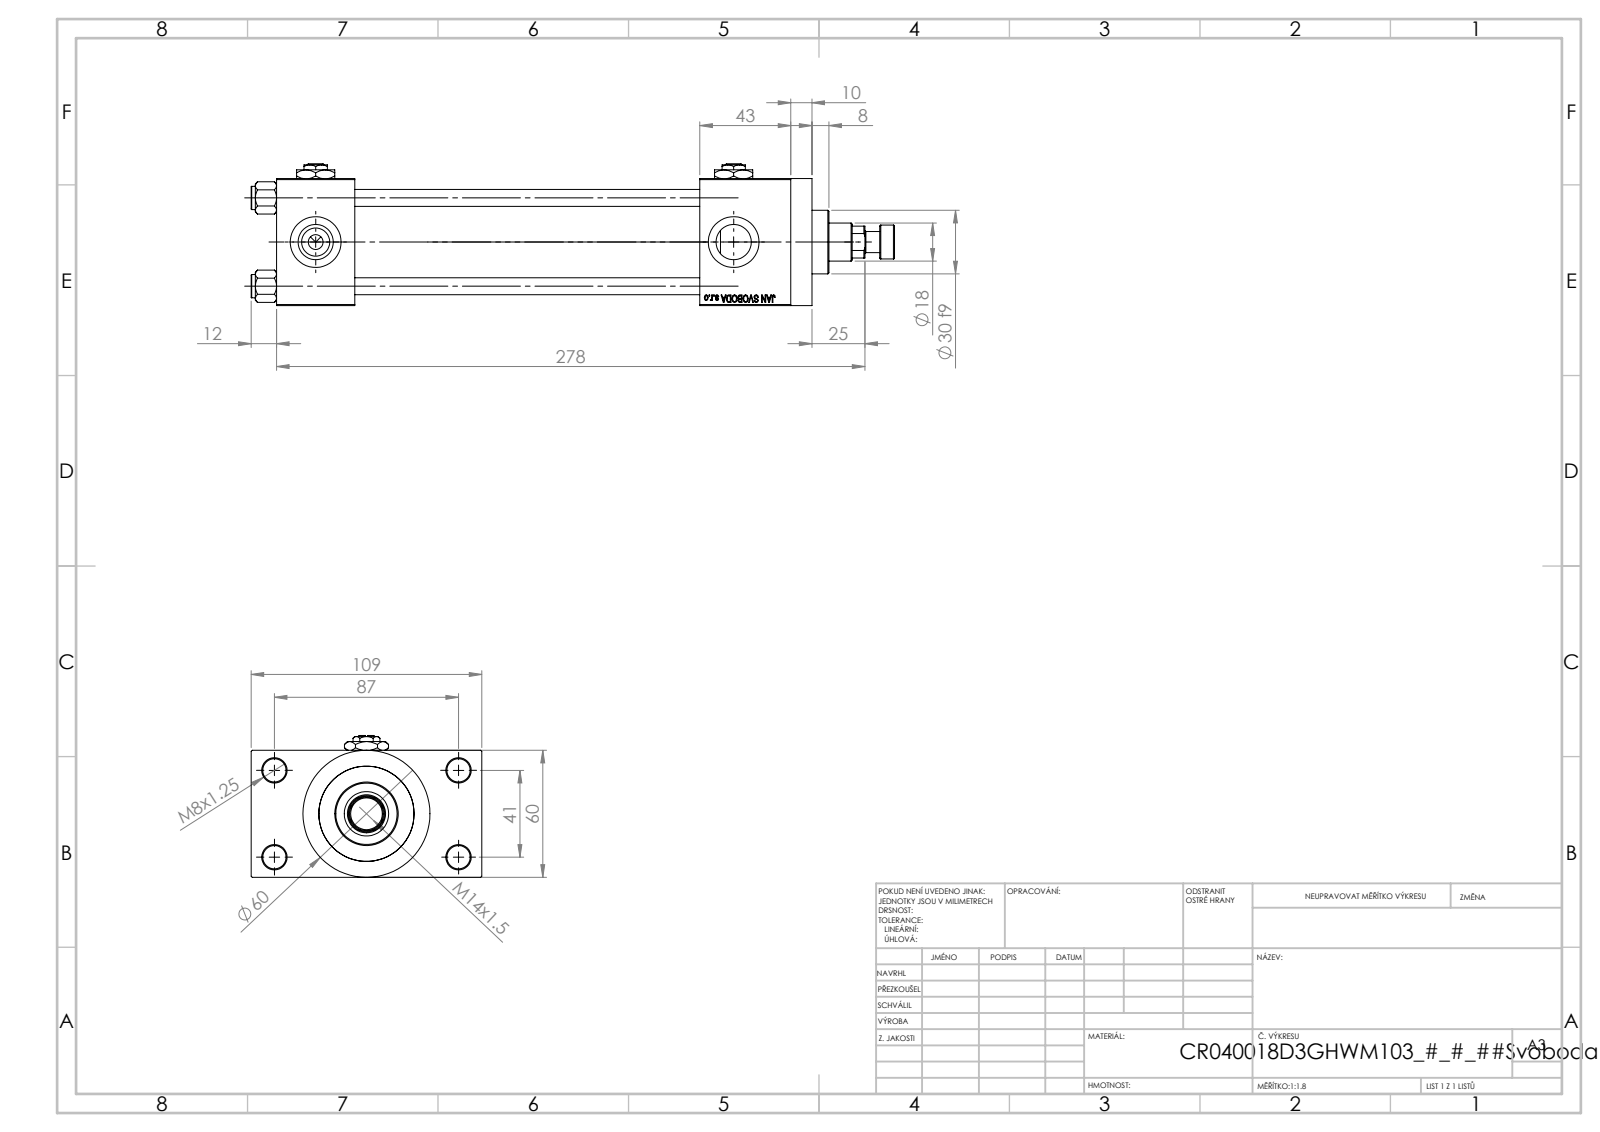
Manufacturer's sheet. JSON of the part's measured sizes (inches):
{"part_name": "NUT_M5_D; V215_VC_A; V215CR_ROD_END_W; V215CR_VCP_D (+3 more)", "step_written_by": "SolidWorks 2019 (CONFIG_CONTROL_DESIGN)", "units": "inches", "bodies": {"solids": 14, "faces": 1218, "planar": 549, "cylindrical": 103, "other": 566}, "overall_size": [11.969, 4.291, 2.638], "volume_in3": 36.78, "surface_area_in2": 265.1, "round_holes": [[0.315, 4], [0.433, 4], [0.656, 4], [0.945, 4], [0.276, 3], [0.335, 1], [0.709, 1], [0.827, 1], [1.22, 1], [1.575, 1], [1.772, 1]], "round_bosses_or_shafts": [[0.433, 4], [2.362, 1], [1.811, 1], [1.181, 1], [0.63, 1], [0.394, 1]], "partial_cylinders_radius": [[0.335, 1]], "face_to_face_distances": [2.362, 0.965, 6.417, 3.327, 1.457, 7.874, 1.693, 9.567, 8.11, 0.394], "hole_center_spacings": [0.892, 1.161, 1.642, 1.856, 1.893, 2.533, 3.011, 1.614]}
